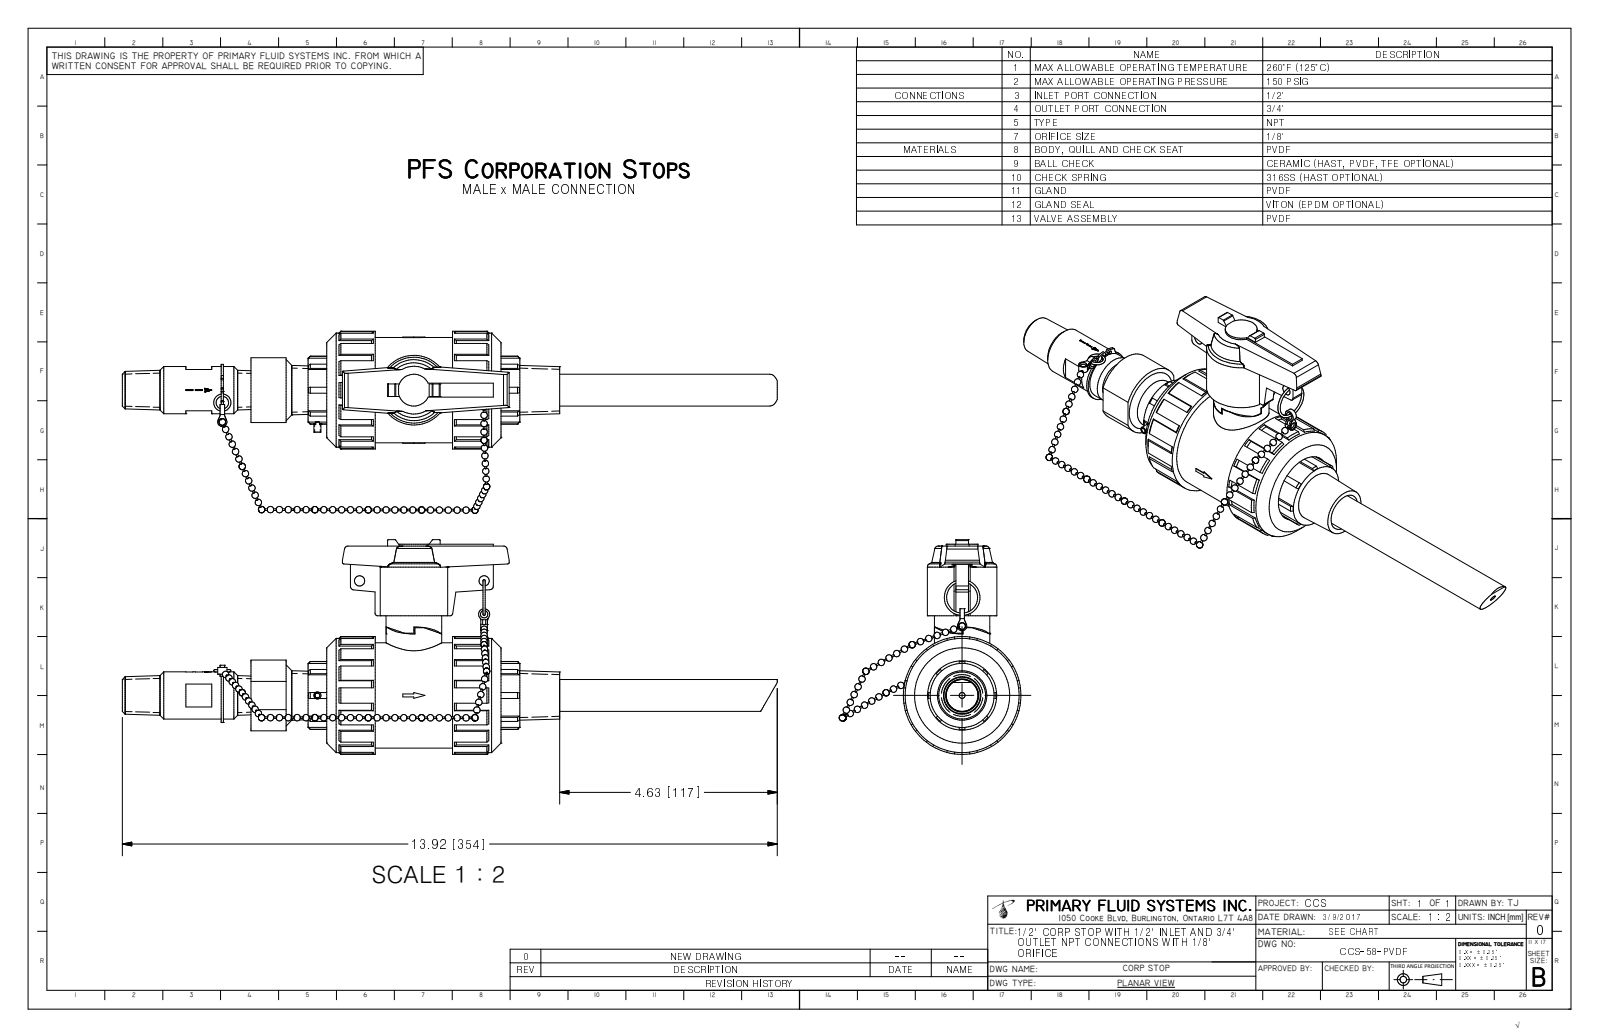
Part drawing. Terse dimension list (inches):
name: CCS-58-PVDF_R0
written by: Autodesk Inventor 2009 (AUTOMOTIVE_DESIGN)
unit: in
bodies: 1 solid, 614 faces (294 planar, 78 cylindrical, 242 other)
size: 13.922 × 4.554 × 3.863
volume: 25.91 in³; area: 122.9 in²
holes: 1× ⌀0.079, 1× ⌀0.125, 1× ⌀0.217, 1× ⌀0.25, 1× ⌀0.469, 1× ⌀0.56, 1× ⌀1.47, 1× ⌀2.16
bosses: 1× ⌀2.5, 1× ⌀2.422, 1× ⌀2.232, 1× ⌀1.801, 1× ⌀1.476, 1× ⌀1.36, 1× ⌀1.181, 1× ⌀1.18
rounds: 4× R0.02, 4× R0.079, 2× R0.039, 2× R0.043, 2× R0.059, 2× R0.157, 1× R0.337, 1× R0.463
face distances: 0.039, 0.266, 0.306, 0.472, 3.233, 0.23, 3.475, 0.242, 3.003, 1.03
hole spacings: 0.535
